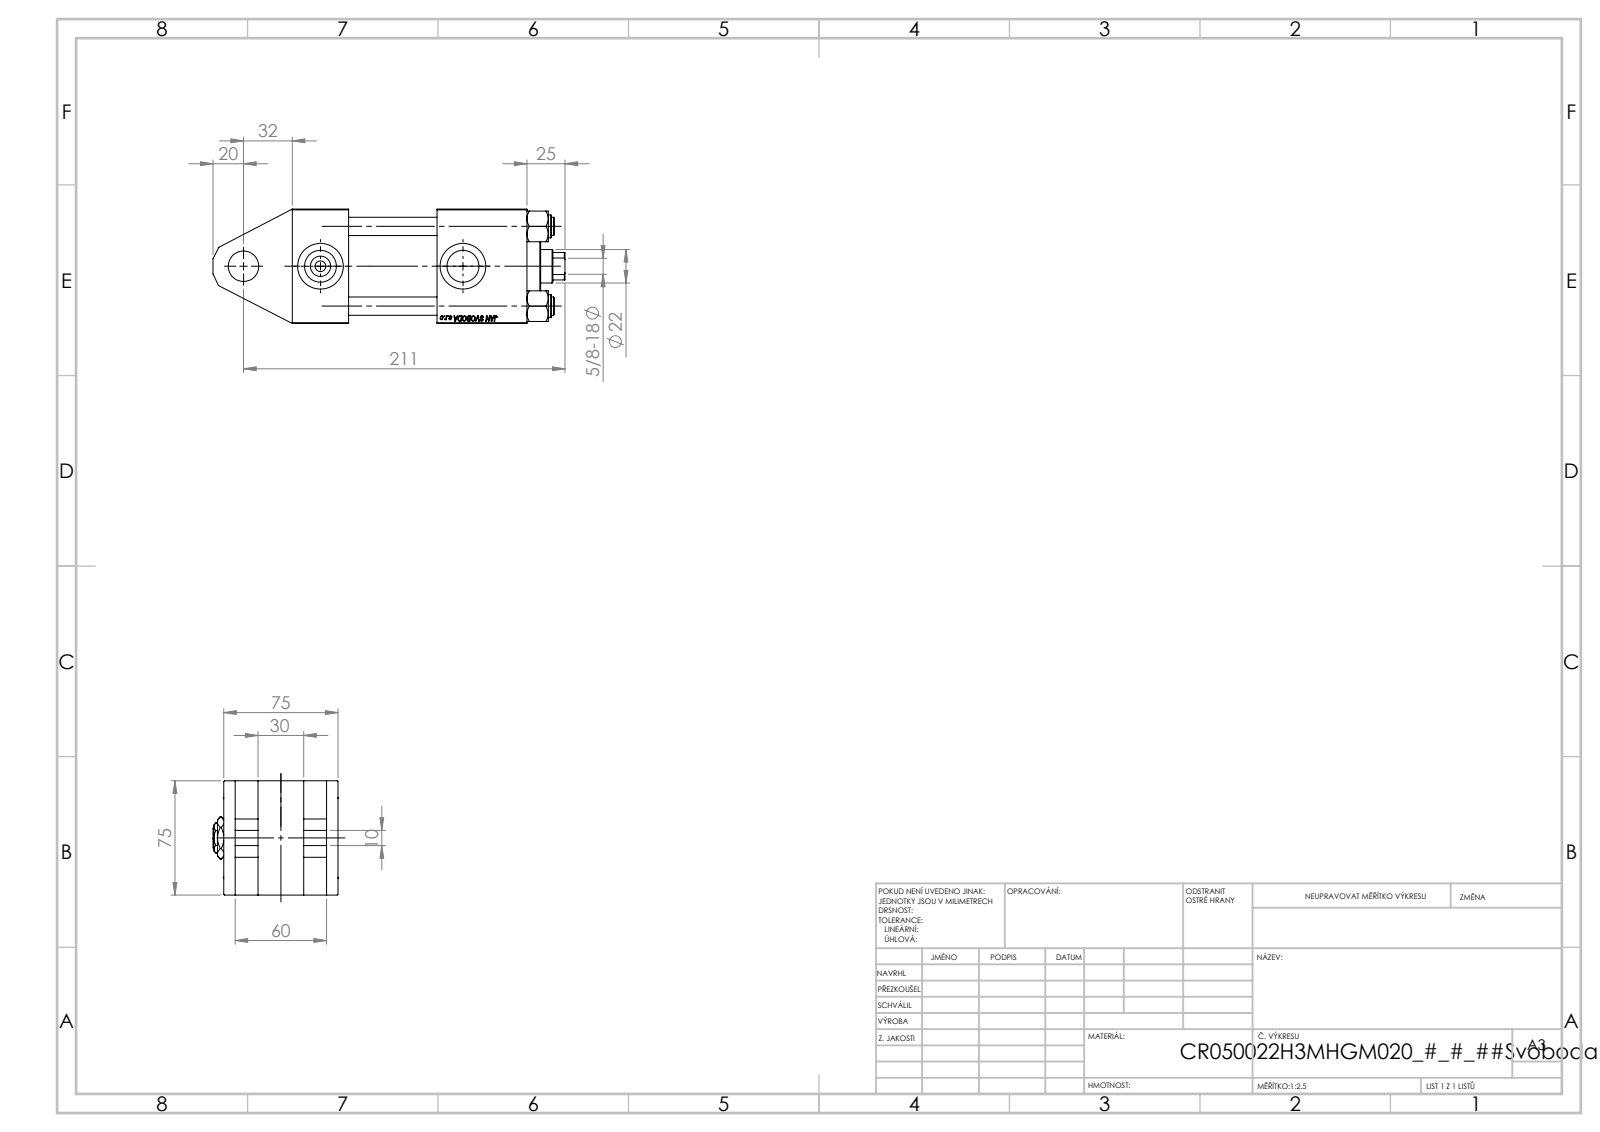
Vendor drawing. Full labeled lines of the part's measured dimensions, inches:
Part name (STEP PRODUCT): V215CR_TYCINKA_H; V215CR_VCP_H; NUT_M5_H; Zatka_pro_OIL_PORT (+2 more)
STEP written by: SolidWorks 2019 (CONFIG_CONTROL_DESIGN)
Units: inches
Bodies: 13 solids, 1229 faces (565 planar, 94 cylindrical, 570 other)
Overall size (bounding box): 9.094 × 3.239 × 2.953
Volume: 44.46 in³ · Surface area: 259.6 in²
Round holes (diameter × count): ⌀0.472 ×4, ⌀0.276 ×2, ⌀0.825 ×2, ⌀1.181 ×2, ⌀0.413 ×1, ⌀0.787 ×1, ⌀0.866 ×1, ⌀0.984 ×1, ⌀1.614 ×1, ⌀1.969 ×1, ⌀2.087 ×1
Round bosses / shafts (diameter × count): ⌀0.591 ×4, ⌀2.205 ×1, ⌀1.339 ×1
Partial cylindrical surfaces — rounded edges, fillets, slot ends (radius × count): R0.413 ×1
Main face-to-face distances: 2.953, 4.606, 0.295, 2.657, 1.772, 0.886, 2.067, 0.591, 2.323, 3.74
Hole centre spacings: 1.456, 2.059, 2.912, 1.988, 3.681, 5.669
